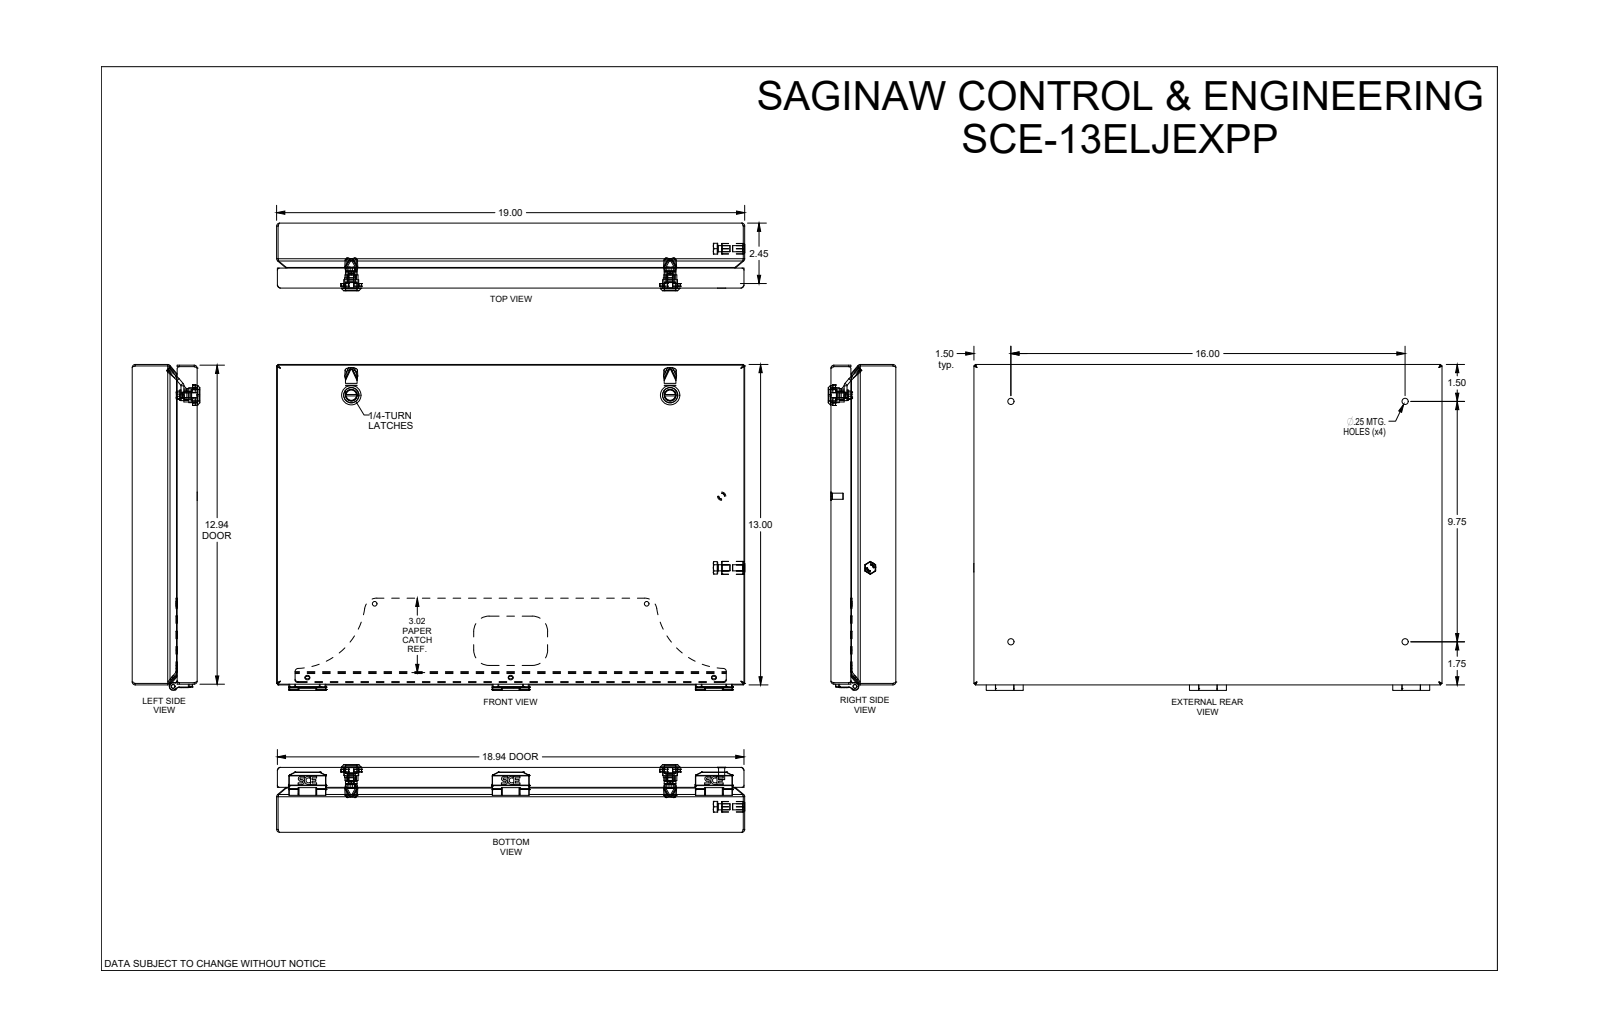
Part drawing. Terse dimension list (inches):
name: SCE-13ELJEXPP
written by: SolidWorks 2019 (AUTOMOTIVE_DESIGN)
unit: in
bodies: 41 solids, 2561 faces (627 planar, 778 cylindrical, 1156 other)
size: 19.004 × 13.22 × 2.742
volume: 49.94 in³; area: 1 601 in²
holes: 6× ⌀0.17, 4× ⌀0.284, 3× ⌀0.02, 3× ⌀0.1, 3× ⌀0.188, 2× ⌀0.187, 2× ⌀0.2, 2× ⌀0.239, 2× ⌀0.254, 2× ⌀0.269, 2× ⌀0.282, 2× ⌀0.326
bosses: 6× ⌀0.479, 6× ⌀0.16, 3× ⌀0.26, 3× ⌀0.237, 3× ⌀0.23, 3× ⌀0.18, 2× ⌀0.788, 2× ⌀0.548
rounds: 198× R0.106, 114× R0.005, 40× R0.03, 36× R0.025, 31× R0.013, 24× R0.015, 18× R0.01, 16× R0.05
face distances: 0.059, 0.06, 2.635, 2.576, 2.575, 2.516, 0.06, 0.798, 12.941, 0.03
hole spacings: 8.25, 16.5, 8.515, 11.088, 11.25, 14.676, 17.251, 20.596
